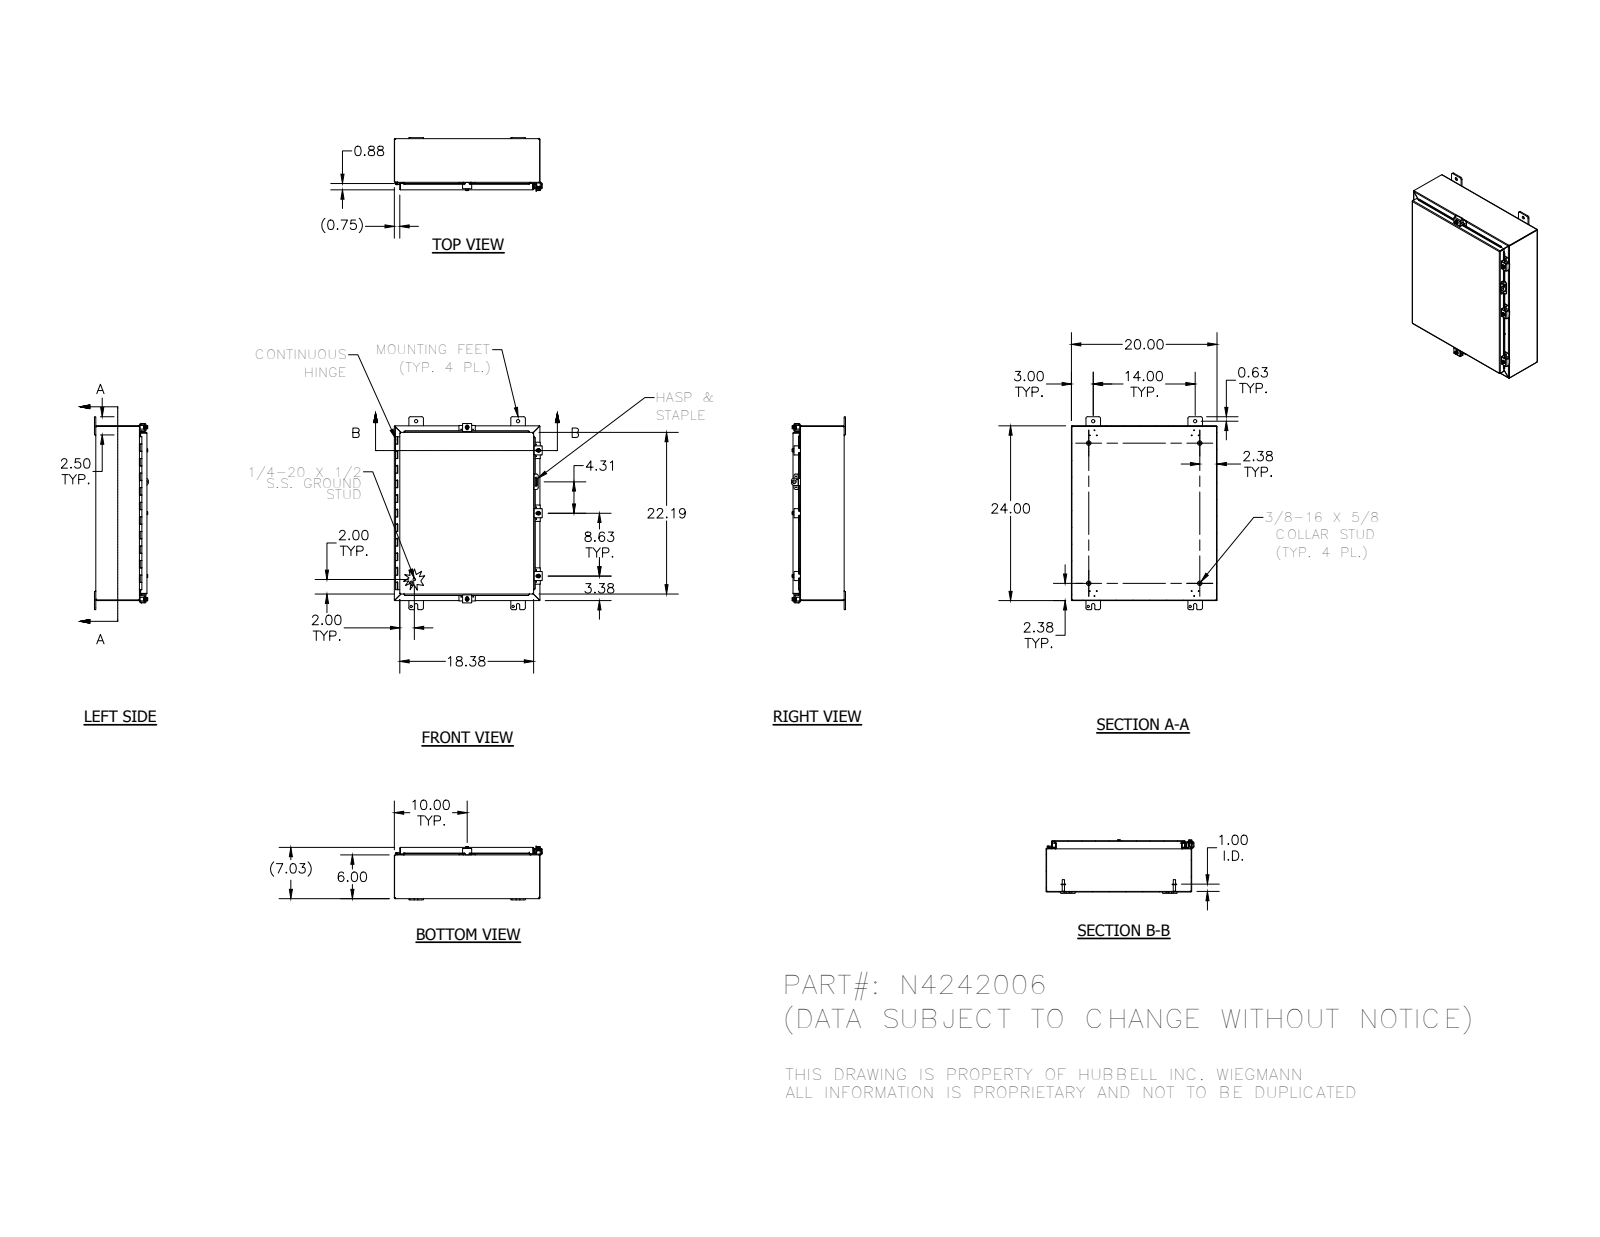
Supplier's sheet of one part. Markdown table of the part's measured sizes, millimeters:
| quantity | value |
| --- | --- |
| part name | 32911_1; 30817_1; N4242006BKP_1; HFW30825-3_1 (+8 more) |
| STEP written by | SolidWorks 2014 (AUTOMOTIVE_DESIGN) |
| units | millimeters |
| bodies | 42 solids, 1854 faces (722 planar, 833 cylindrical, 299 other) |
| overall size | 673.1 × 515.9 × 188.2 |
| volume | 2 314 000 mm³ |
| surface area | 2 366 000 mm² |
| round holes (diameter × count) | 2.8 × 13, 3 × 12, 5.4 × 5, 7.1 × 5, 7.6 × 5, 8 × 4, 11.1 × 4, 3.2 × 1, 4 × 1, 12.7 × 1 |
| round bosses / shafts (diameter × count) | 6.4 × 7, 13.2 × 5, 12.7 × 5, 8.9 × 5, 15.9 × 4, 8.4 × 4, 2.9 × 2, 8.6 × 1 |
| partial cylindrical surfaces (radius × count) | 0.8 × 61, 1.6 × 37, 3.2 × 35, 6.4 × 31, 0.8 × 23, 2.7 × 23, 3.6 × 10, 1.6 × 8 |
| main face-to-face distances | 1.9, 176.8, 174.9, 178.6, 506.1, 607.7, 150.5, 26.2, 504.2, 508 |
| hole center spacings | 355.6, 22.3, 19.3, 21.3, 23.9, 24.6, 40.5, 50.7 |
